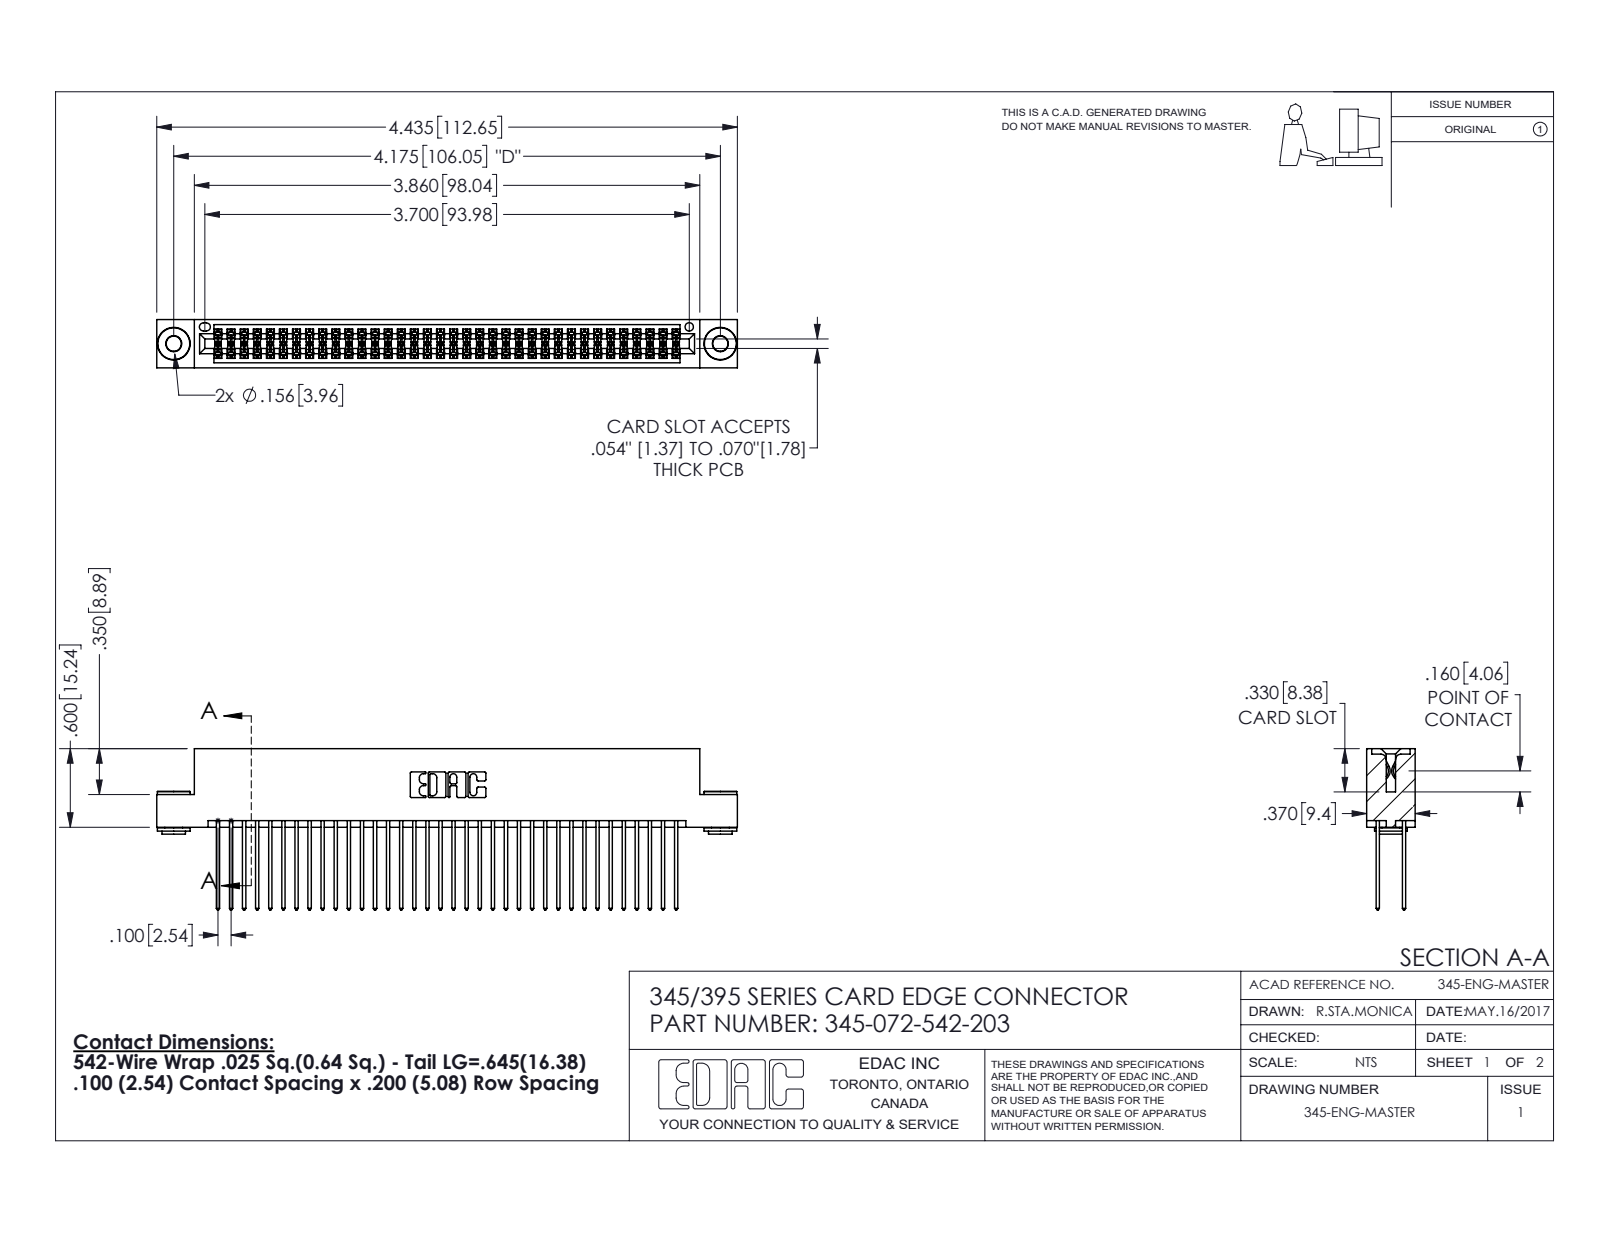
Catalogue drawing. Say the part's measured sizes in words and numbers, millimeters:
The part is named "345 Part_Flush Mounting Lugs - 0.156 Dia-TH; 345-292-001_345-293-142; 345-250-002_345-250-002-102; 345-072-542-203". Its 3-D file was written by "SolidWorks 2016 (CONFIG_CONTROL_DESIGN)". It is 75 solids with 3764 faces: 2466 planar, 1290 cylindrical and 8 other. Overall it measures 112.6 by 31.3 by 9.4 millimeters. Its volume is 11 200 cubic millimeters and its surface area 18 280 square millimeters. Round holes: 2 of diameter 2.9, 2 of diameter 4, 1 of diameter 1.6. Round bosses or shafts: 2 of diameter 6.4, 2 of diameter 4.6, 2 of diameter 3.5. Partial cylindrical surfaces (rounded edges, fillets, slot ends): 108 of radius 0.2, 72 of radius 0.3, 22 of radius 0.3, 6 of radius 0.2, 6 of radius 0.8, 3 of radius 0.7, 2 of radius 0.4, 2 of radius 0.5. The main face-to-face distances are 1.8, 7.6, 5.1, 0.6, 2.5, 6.9, 5.7, 9.4, 4.4, 3.8. The hole center spacings are 6.9, 100.1, 106.
